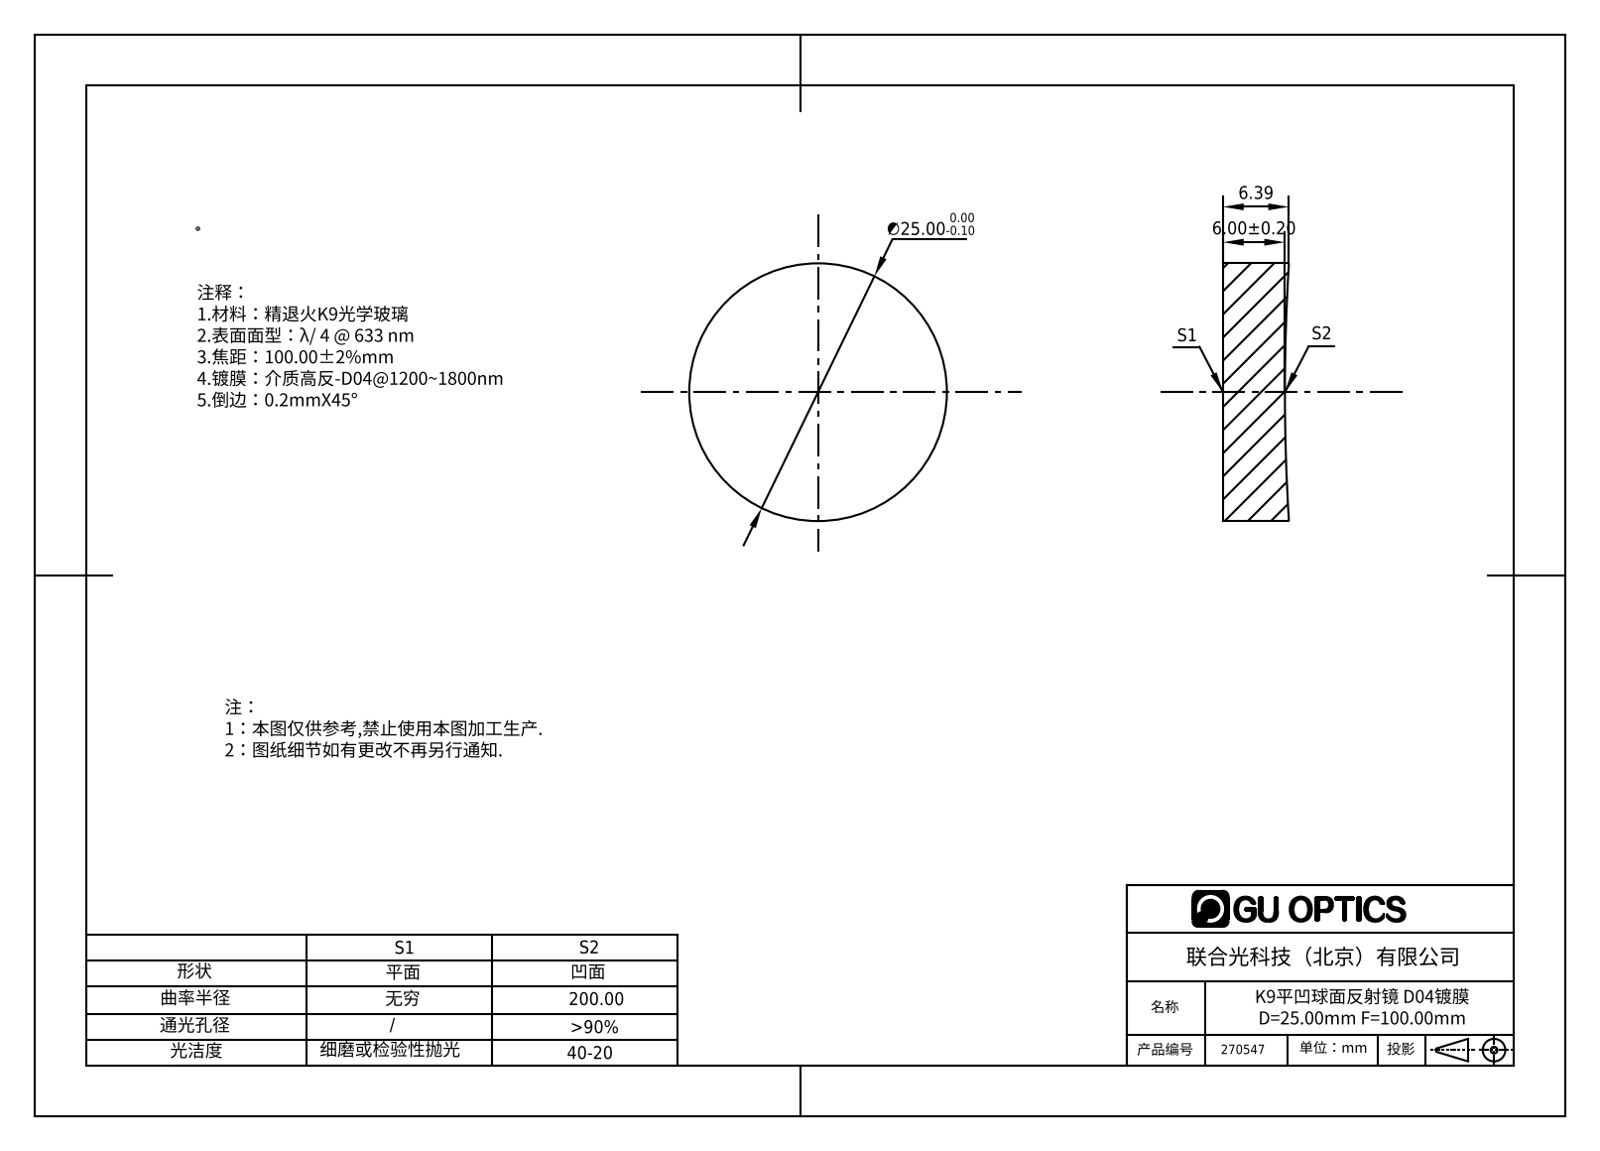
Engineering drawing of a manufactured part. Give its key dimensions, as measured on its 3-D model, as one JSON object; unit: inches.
{"part_name": "270027", "step_written_by": "SolidWorks 2016 (AUTOMOTIVE_DESIGN)", "units": "inches", "bodies": {"solids": 1, "faces": 5, "planar": 1, "cylindrical": 2, "other": 2}, "overall_size": [0.984, 0.984, 0.252], "volume_in3": 0.186, "surface_area_in2": 2.3, "round_bosses_or_shafts": [[0.984, 1]]}
